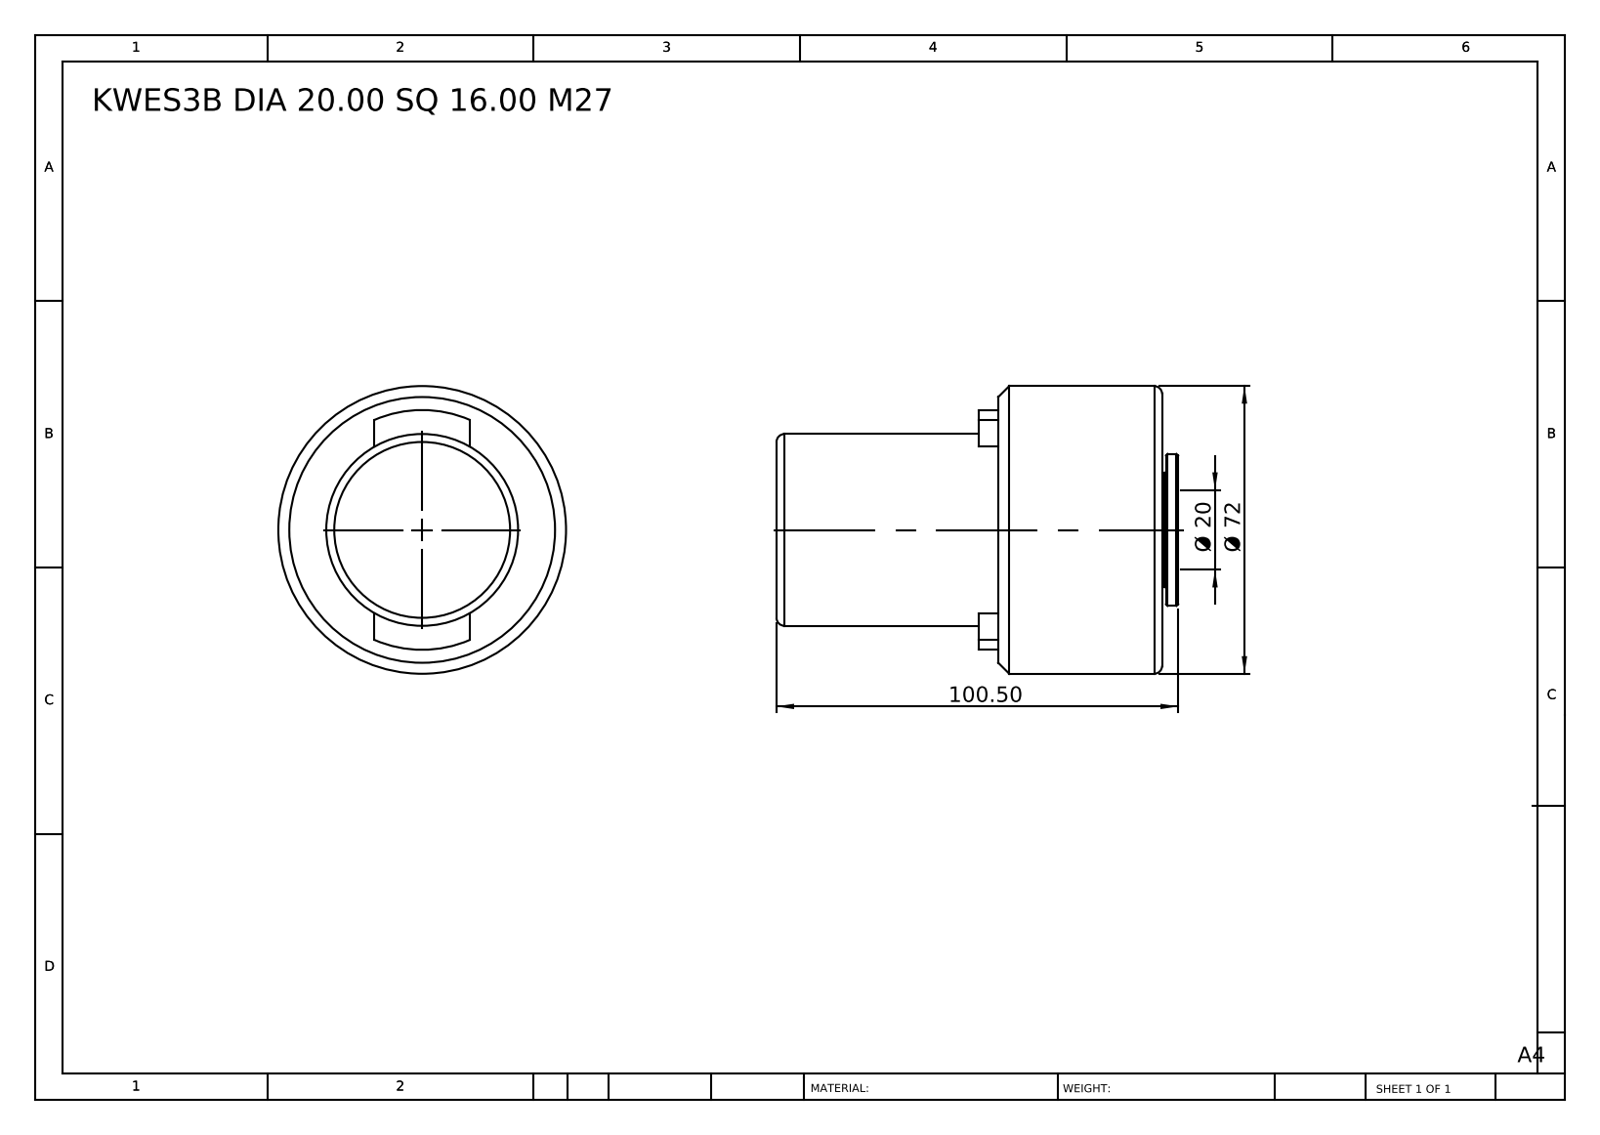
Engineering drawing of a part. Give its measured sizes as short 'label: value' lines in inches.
name: KWES3B DIA 20.00 SQ 16.00 1'''''''' UNC
written by: SolidWorks 2014 (CONFIG_CONTROL_DESIGN)
unit: in
bodies: 1 solid, 39 faces (12 planar, 13 cylindrical, 14 other)
size: 3.957 × 2.835 × 2.835
volume: 15.81 in³; area: 45.07 in²
holes: 1× ⌀0.787
bosses: 1× ⌀2.835, 1× ⌀1.89, 1× ⌀1.496, 1× ⌀1.122
rounds: 1× R1.181
face distances: 3.799, 2.185, 1.614, 3.957, 1.772, 0.157, 0.197, 3.839, 1.654, 0.039
